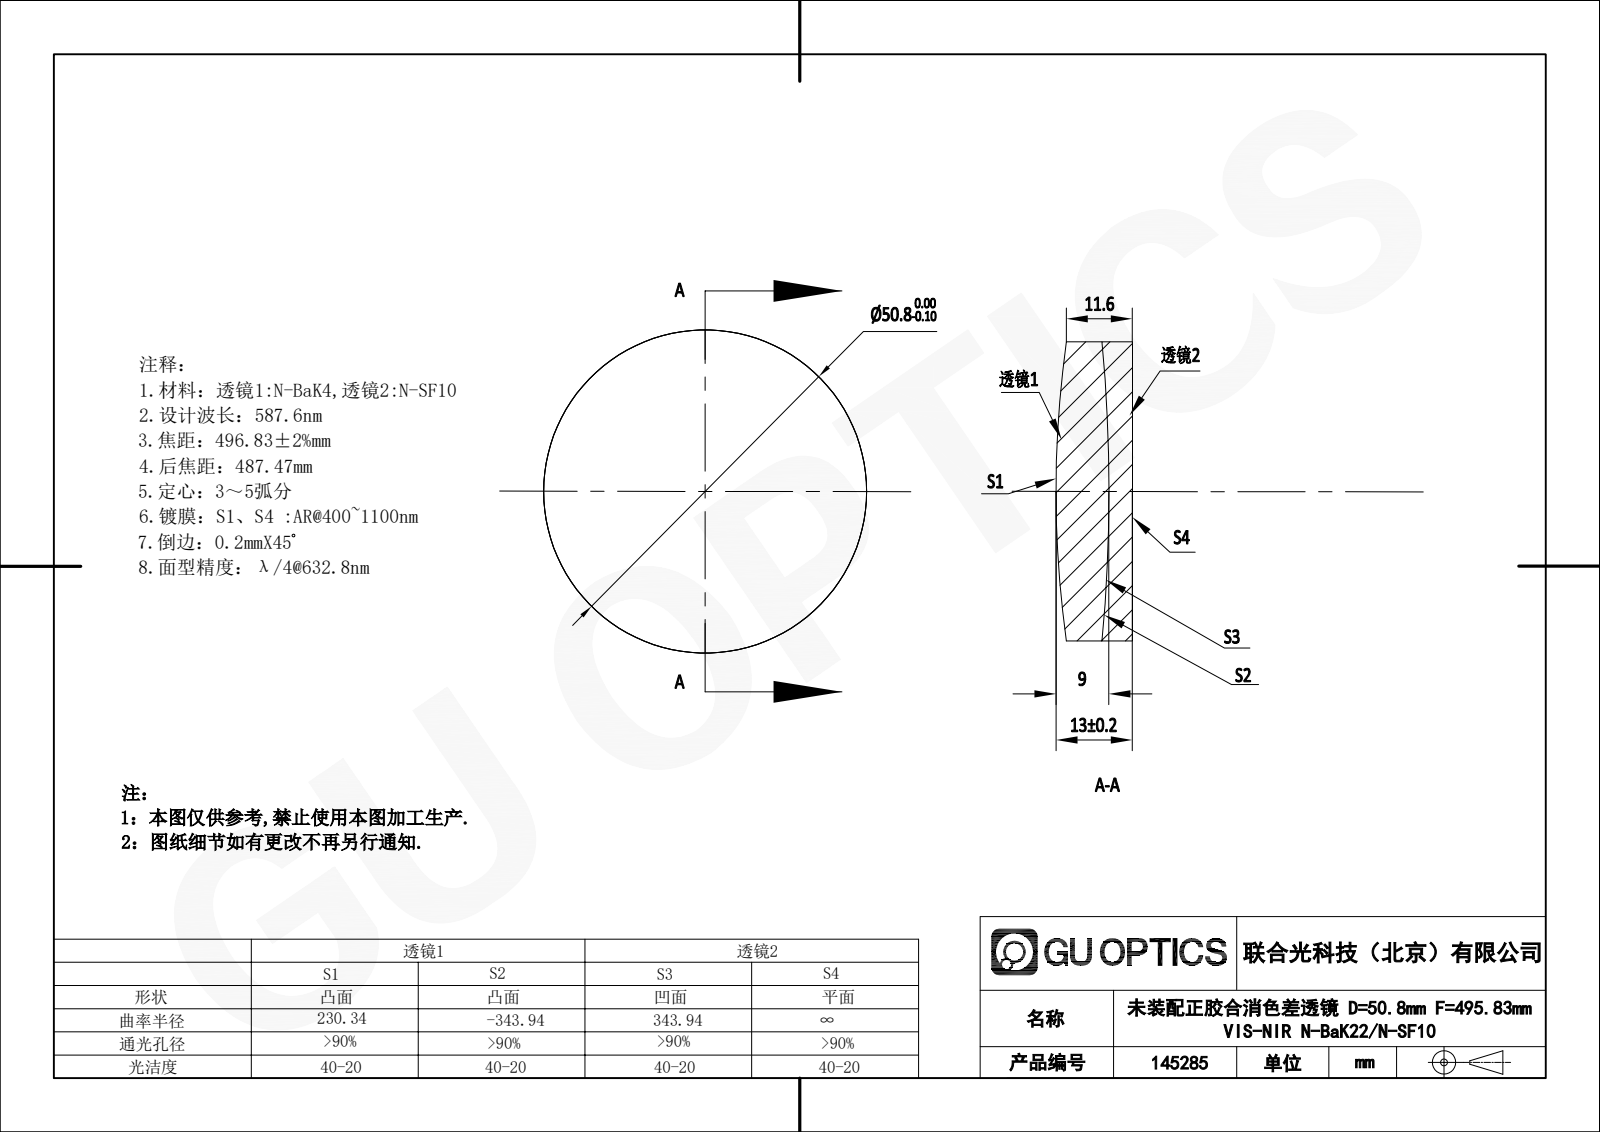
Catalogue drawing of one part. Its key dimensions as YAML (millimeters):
part_name: "145285"
step_written_by: "SolidWorks 2020 (CONFIG_CONTROL_DESIGN)"
units: millimeters
bodies: {solids: 2, faces: 11, planar: 1, cylindrical: 4, other: 6}
overall_size: [50.8, 50.8, 12.53]
volume: 24451
surface_area: 9892
round_bosses_or_shafts:
  - {diameter: 50.8, count: 1}
